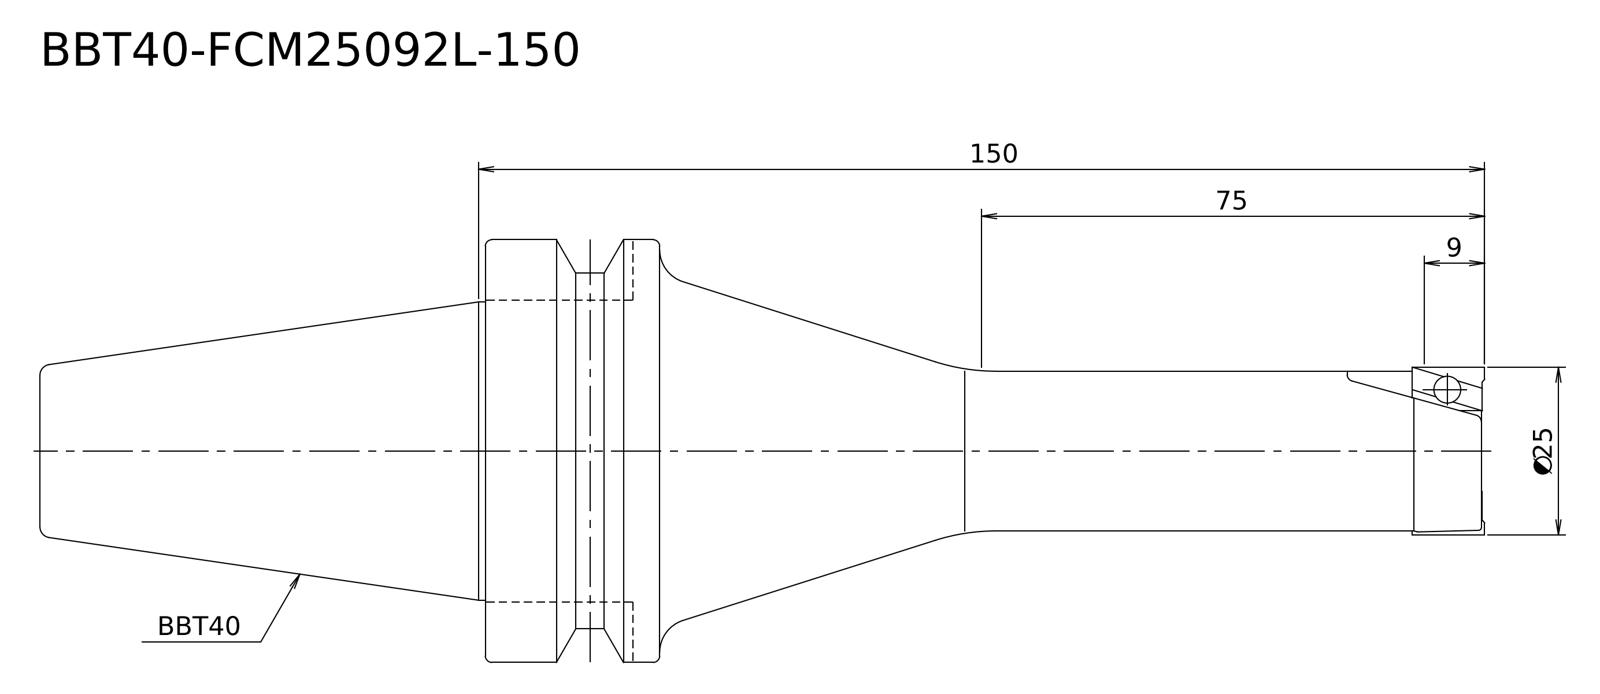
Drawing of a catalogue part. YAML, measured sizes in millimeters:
step_written_by: "Kubotek KeyCreator V8.5.1 (14335) (CONFIG_CONTROL_DESIGN)"
units: millimeters
bodies: {solids: 1, faces: 17, planar: 4, cylindrical: 6, other: 7}
overall_size: [215.4, 63, 63]
volume: 231224
surface_area: 28234
round_bosses_or_shafts:
  - {diameter: 63, count: 1}
  - {diameter: 53, count: 1}
  - {diameter: 44.45, count: 1}
  - {diameter: 25, count: 1}
  - {diameter: 23.8, count: 1}
face_to_face_distances: [66.4, 149, 215.4, 123, 26, 92.4]
